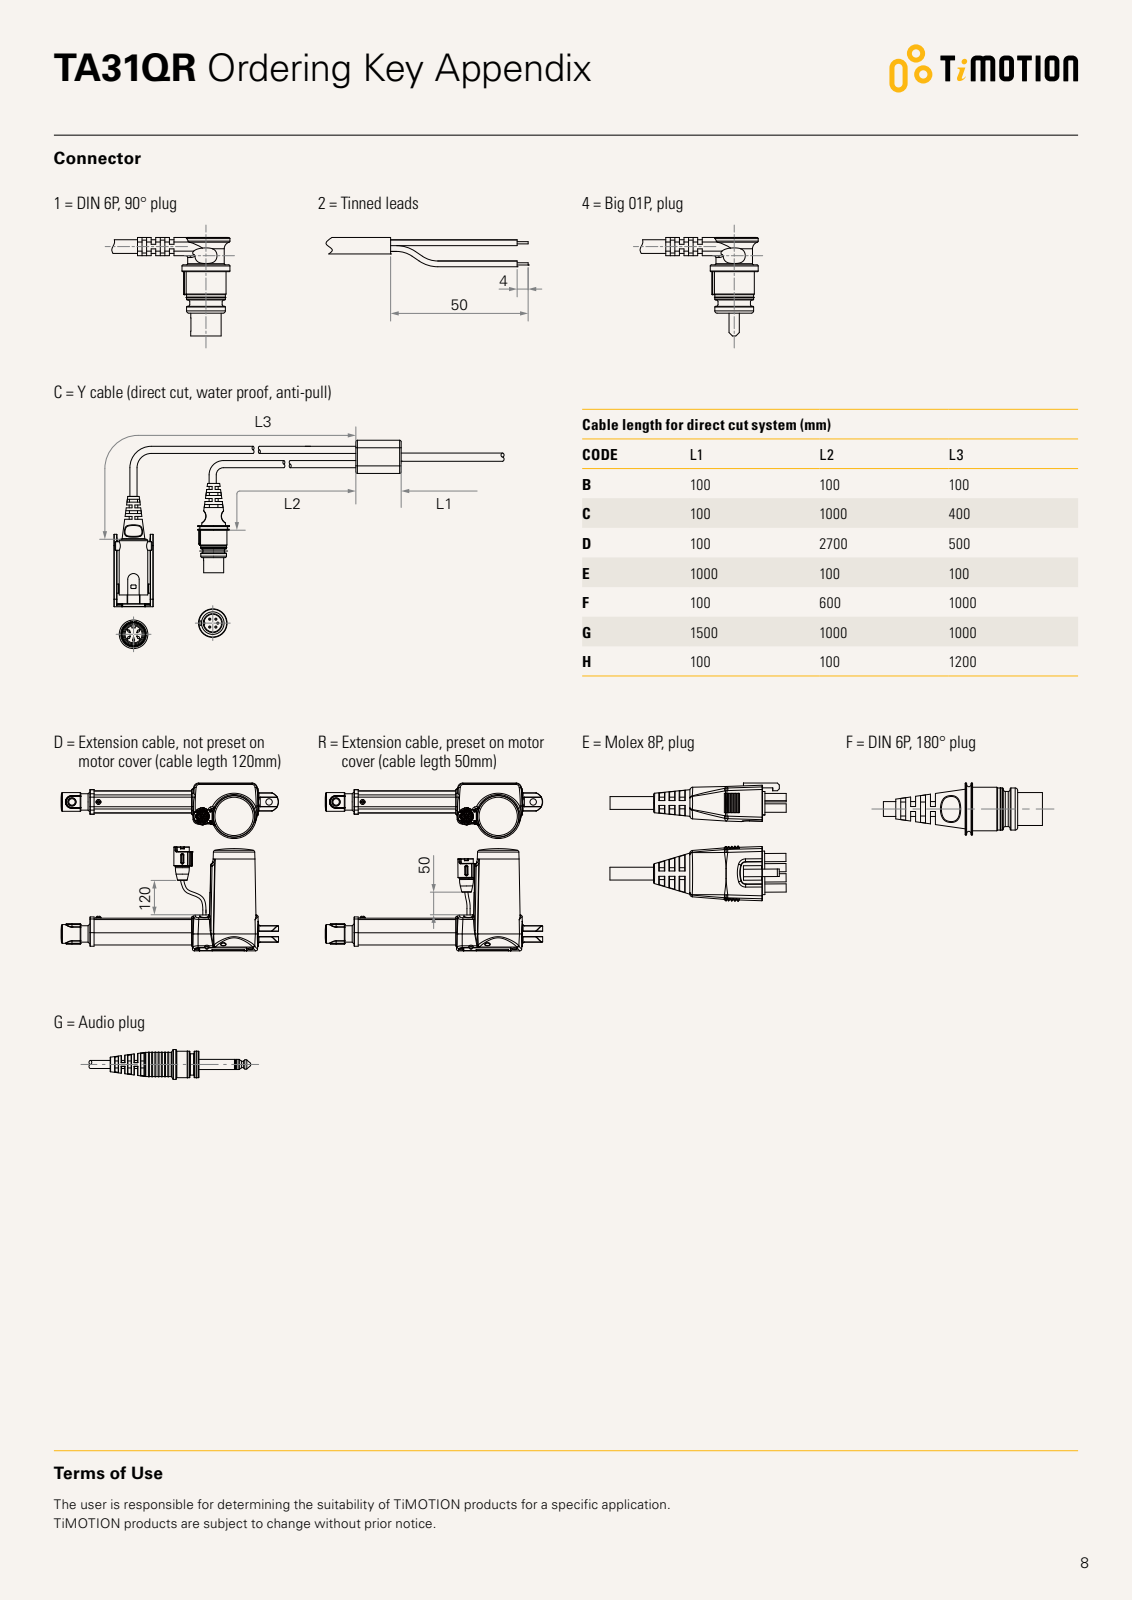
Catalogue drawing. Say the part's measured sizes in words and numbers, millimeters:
The part is named "三維零件圖-31605-794-外殼護蓋-0; 32109-0102-內管-0; 三維零件圖-32209-4501-外管-0; 3D_TA31QR (+8 more)". Its 3-D file was written by "SolidWorks 2015 (CONFIG_CONTROL_DESIGN)". It is 11 solids with 4687 faces: 1660 planar, 936 cylindrical and 2091 other. Overall it measures 459.51 by 187.35 by 88.89 millimeters. Its volume is 271 402 cubic millimeters and its surface area 340 429 square millimeters. Round holes: 33 of diameter 1, 12 of diameter 4.2, 9 of diameter 3.3, 4 of diameter 5.3, 4 of diameter 8, 2 of diameter 2.6, 2 of diameter 5, 2 of diameter 25, 1 of diameter 2.71, 1 of diameter 3, 1 of diameter 3.25, 1 of diameter 3.4. Round bosses or shafts: 2 of diameter 12, 2 of diameter 7.5, 1 of diameter 35, 1 of diameter 32.6, 1 of diameter 26, 1 of diameter 24, 1 of diameter 14, 1 of diameter 6. Partial cylindrical surfaces (rounded edges, fillets, slot ends): 91 of radius 0.5, 70 of radius 0.2, 34 of radius 1, 26 of radius 0.3, 26 of radius 2, 21 of radius 0.1, 12 of radius 3, 9 of radius 0.6. The main face-to-face distances are 1.2, 2.8, 13, 56, 1.35, 54.65, 53.2, 18, 67.65, 29.6. The hole center spacings are 4.47, 2, 2.83, 4, 6.32, 16.45, 5.66, 7.21.
